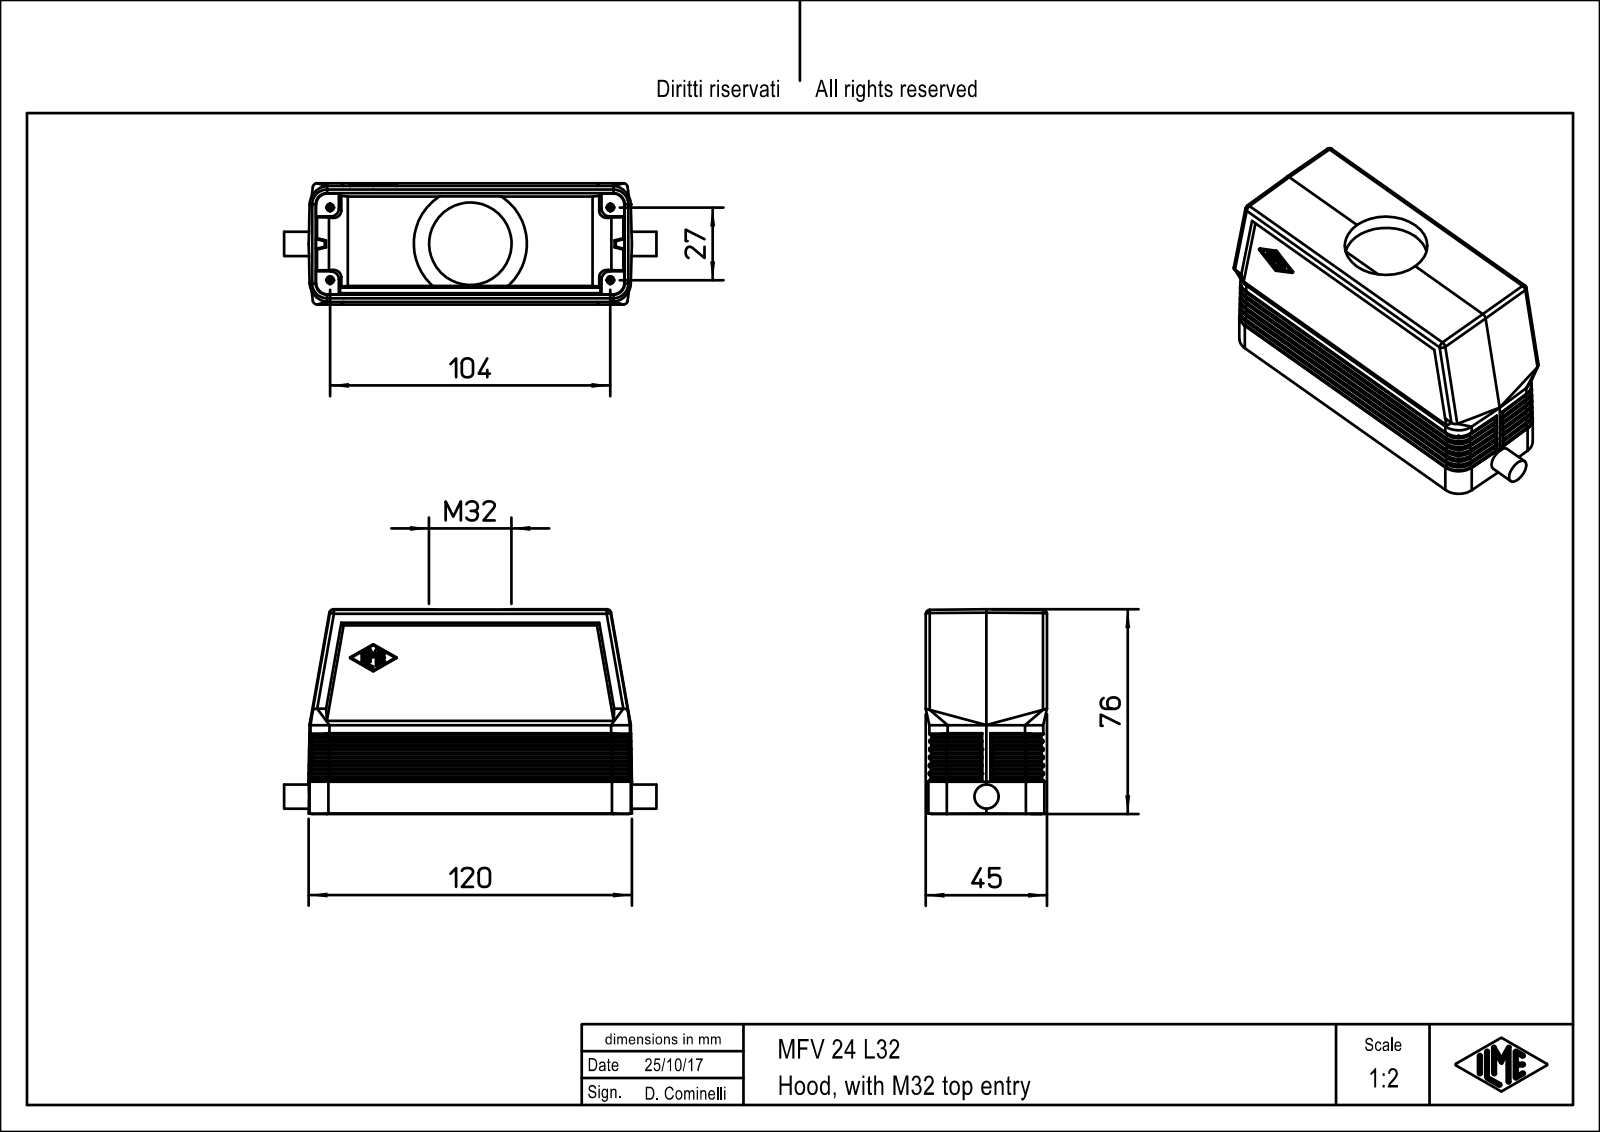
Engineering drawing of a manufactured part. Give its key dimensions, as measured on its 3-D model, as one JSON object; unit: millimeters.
{"part_name": "MFV_24_L32", "step_written_by": "PTC Creo Elements/Direct Modeling 19.0E 27-Jun-2016 (C) Parametric Technology GmbH (AUTOMOTIVE_DESIGN)", "units": "millimeters", "bodies": {"solids": 1, "faces": 511, "planar": 236, "cylindrical": 139, "other": 136}, "overall_size": [138.2, 76, 45], "volume_mm3": 107454, "surface_area_mm2": 54188, "round_holes": [[30.6, 1]], "round_bosses_or_shafts": [[9, 1]], "partial_cylinders_radius": [[0.5, 78], [0.33, 15], [1.5, 10], [7, 8], [3, 4], [4.2, 4], [0.17, 3], [0.67, 1]], "face_to_face_distances": [43, 2.01, 2, 4, 1, 44, 8.45, 6, 6.01, 4.01]}
